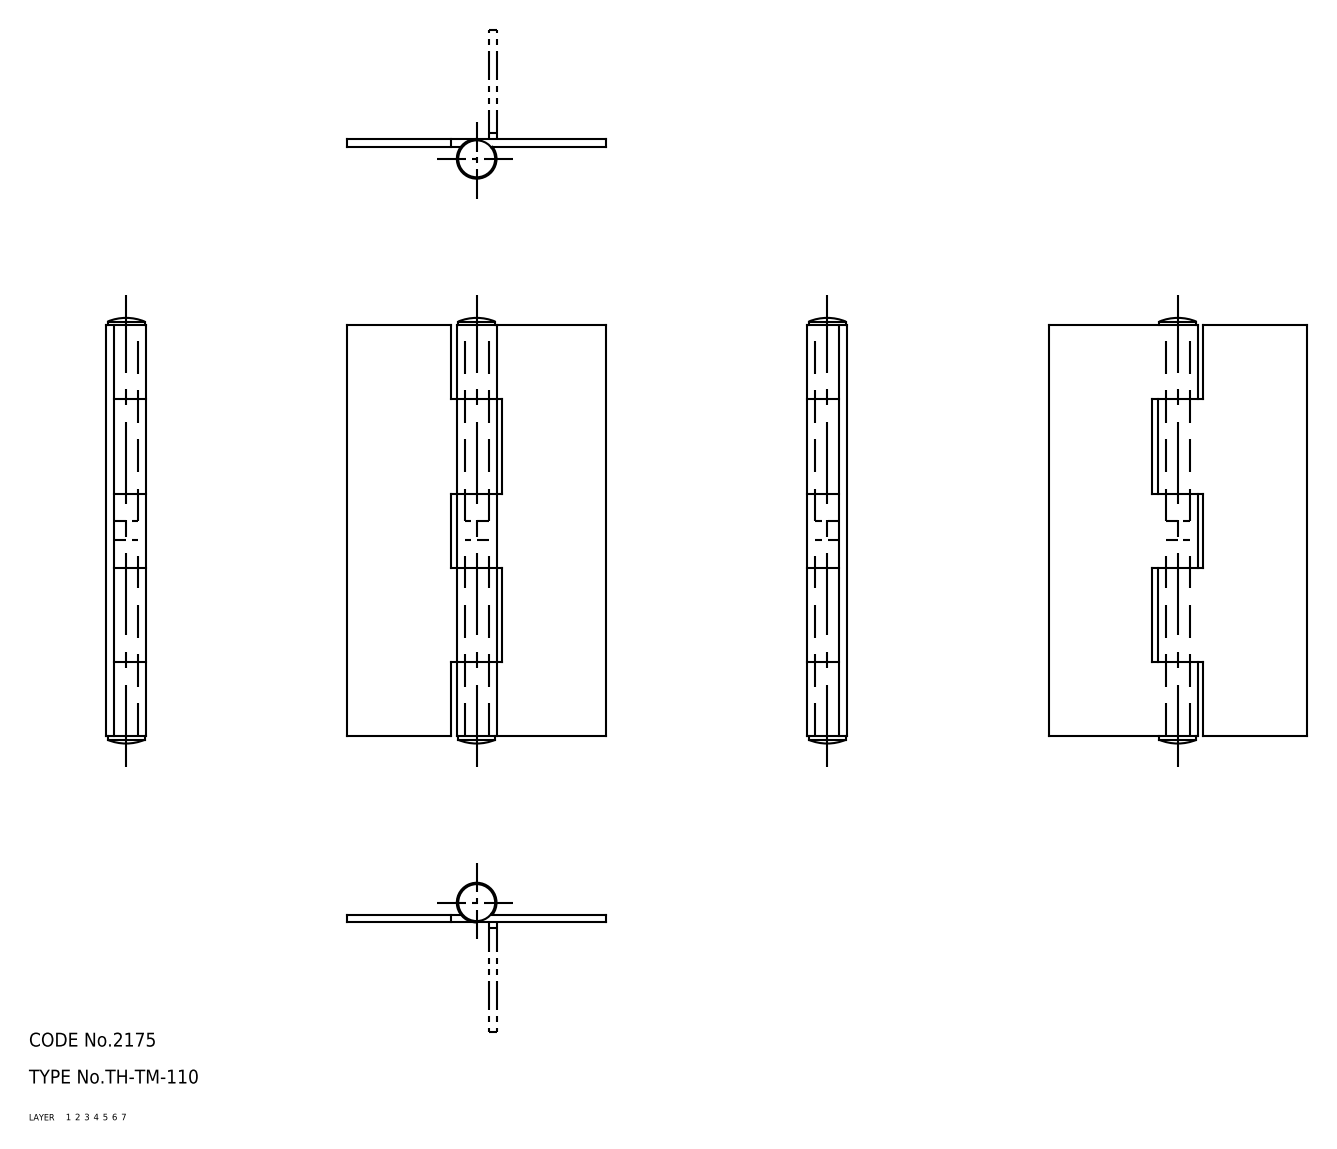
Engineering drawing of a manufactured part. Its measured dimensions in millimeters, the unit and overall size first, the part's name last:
Units: millimetres
Overall size (bounding box): 92.2 × 56 × 8.6
Volume: 12 362 mm³ · Surface area: 15 074 mm²
Bodies: 4 solids, 52 faces (0 planar, 0 cylindrical, 52 other)
Part name (STEP PRODUCT): 67111532; 67111545; 67111558; 67111571
STEP written by: CADfix (AUTOMOTIVE_DESIGN)
